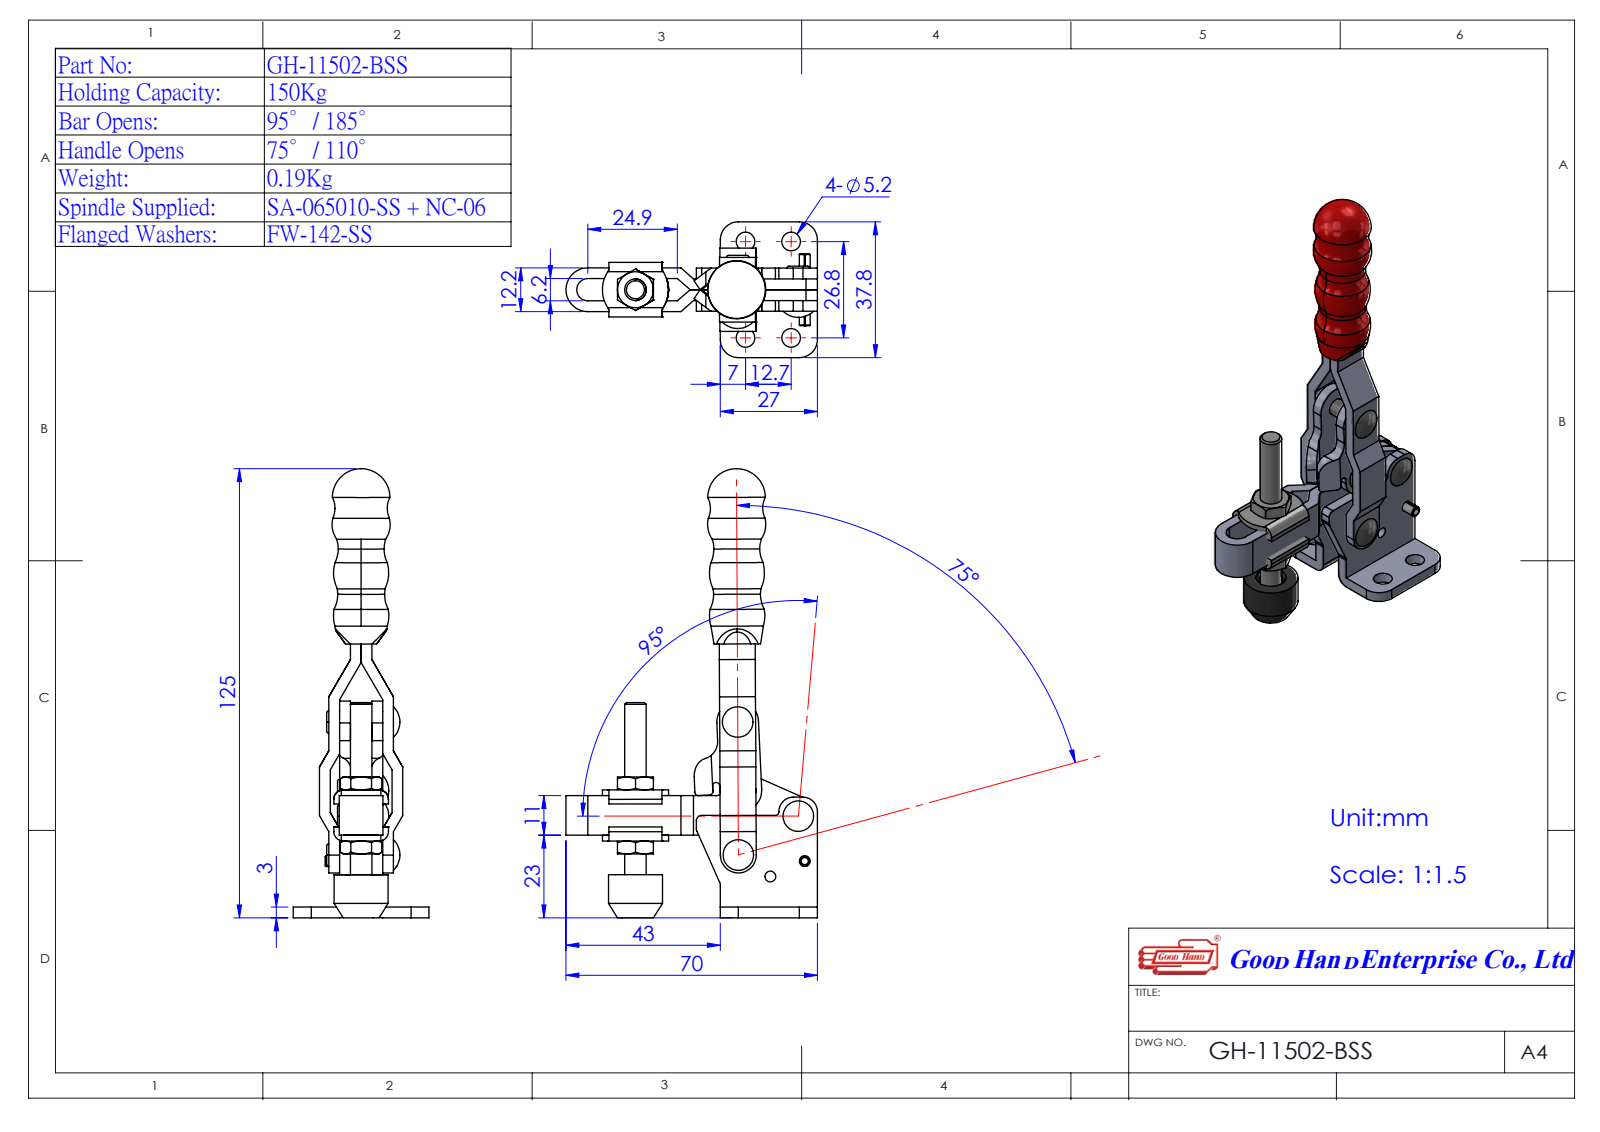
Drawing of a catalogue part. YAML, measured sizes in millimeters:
part_name: "Group5^493805(GH-11502-BSS); 111502B08-1^493805(GH-11502-BSS); Group2^493805(GH-11502-BSS); Group1^493805(GH-11502-BSS) (+2 more)"
step_written_by: "SolidWorks 2016 (AUTOMOTIVE_DESIGN)"
units: millimeters
bodies: {solids: 8, faces: 301, planar: 141, cylindrical: 92, other: 68}
overall_size: [125.01, 70, 37.8]
volume: 31959
surface_area: 22371
round_holes:
  - {diameter: 5.2, count: 4}
  - {diameter: 3, count: 3}
  - {diameter: 4.83, count: 1}
round_bosses_or_shafts:
  - {diameter: 4.85, count: 2}
  - {diameter: 15, count: 1}
  - {diameter: 6, count: 1}
  - {diameter: 3, count: 1}
partial_cylinders:
  - {radius: 1, count: 8}
  - {radius: 5, count: 6}
  - {radius: 2.6, count: 4}
  - {radius: 2, count: 2}
  - {radius: 4, count: 2}
  - {radius: 5.3, count: 2}
  - {radius: 5.8, count: 2}
  - {radius: 1.5, count: 1}
face_to_face_distances: [3, 6, 9, 12, 3.1, 6.1, 9.1, 12.1, 2.9, 5.6]
hole_center_spacings: [12.7, 26.8, 29.66, 17.5, 17.91, 19.12, 19.89, 31.17]
